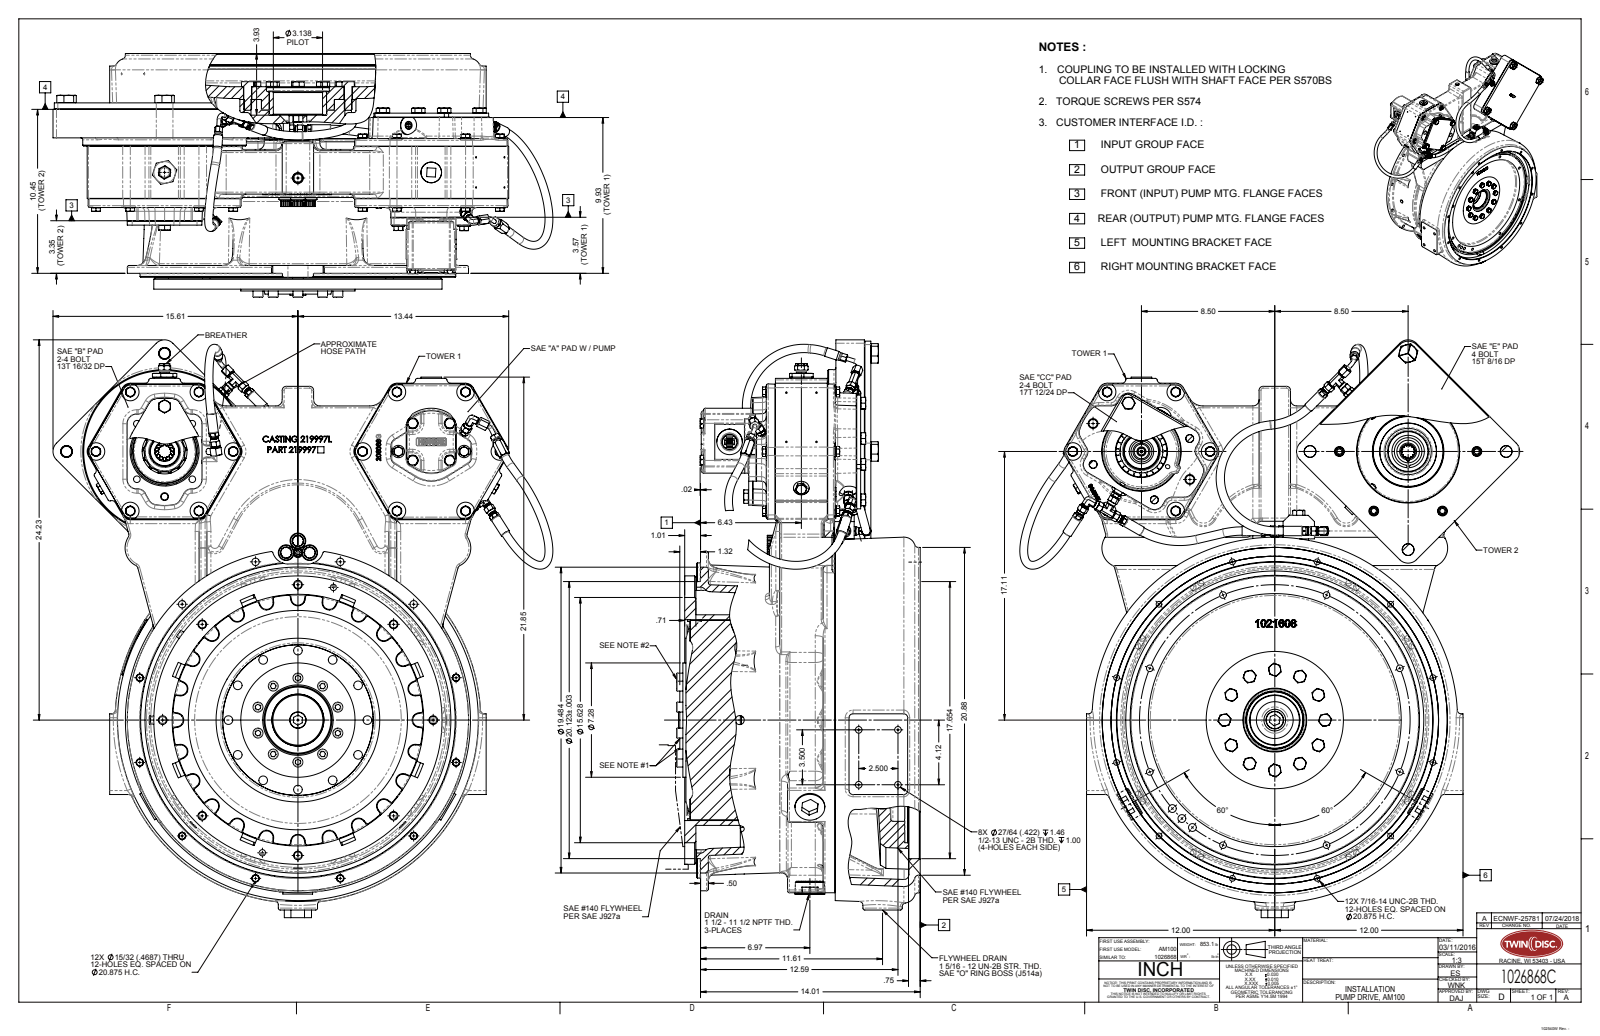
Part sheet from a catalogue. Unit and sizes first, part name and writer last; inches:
Units: inches
Overall size (bounding box): 36.812 × 31.867 × 15.525
Round holes (diameter × count): ⌀0.472 ×20, ⌀0.422 ×16, ⌀0.368 ×12, ⌀0.437 ×8, ⌀0.551 ×8, ⌀0.578 ×4, ⌀0.5 ×3, ⌀0.625 ×3, ⌀1 ×3, ⌀0.107 ×2, ⌀0.402 ×2, ⌀0.75 ×2
Round bosses / shafts (diameter × count): ⌀0.62 ×14, ⌀0.743 ×10, ⌀0.63 ×10, ⌀0.364 ×8, ⌀0.53 ×7, ⌀0.437 ×7, ⌀0.601 ×6, ⌀0.492 ×6
Partial cylindrical surfaces — rounded edges, fillets, slot ends (radius × count): R0.12 ×82, R0.25 ×68, R0.1 ×46, R0.5 ×45, R0.42 ×24, R0.56 ×20, R0.079 ×17, R0.459 ×15
Main face-to-face distances: 4.196, 2.271, 6.467, 5.81, 3.539, 0.657, 8.589, 2.763, 3.046, 0.776
Hole centre spacings: 20.164, 10.437, 10.438, 18.078, 14.761, 20.875, 5.403, 14.761
Bodies: 0 solids, 3639 faces (1347 planar, 1024 cylindrical, 1268 other)
Part name (STEP PRODUCT): 1026868C
STEP written by: SolidWorks 2015 (AUTOMOTIVE_DESIGN)
